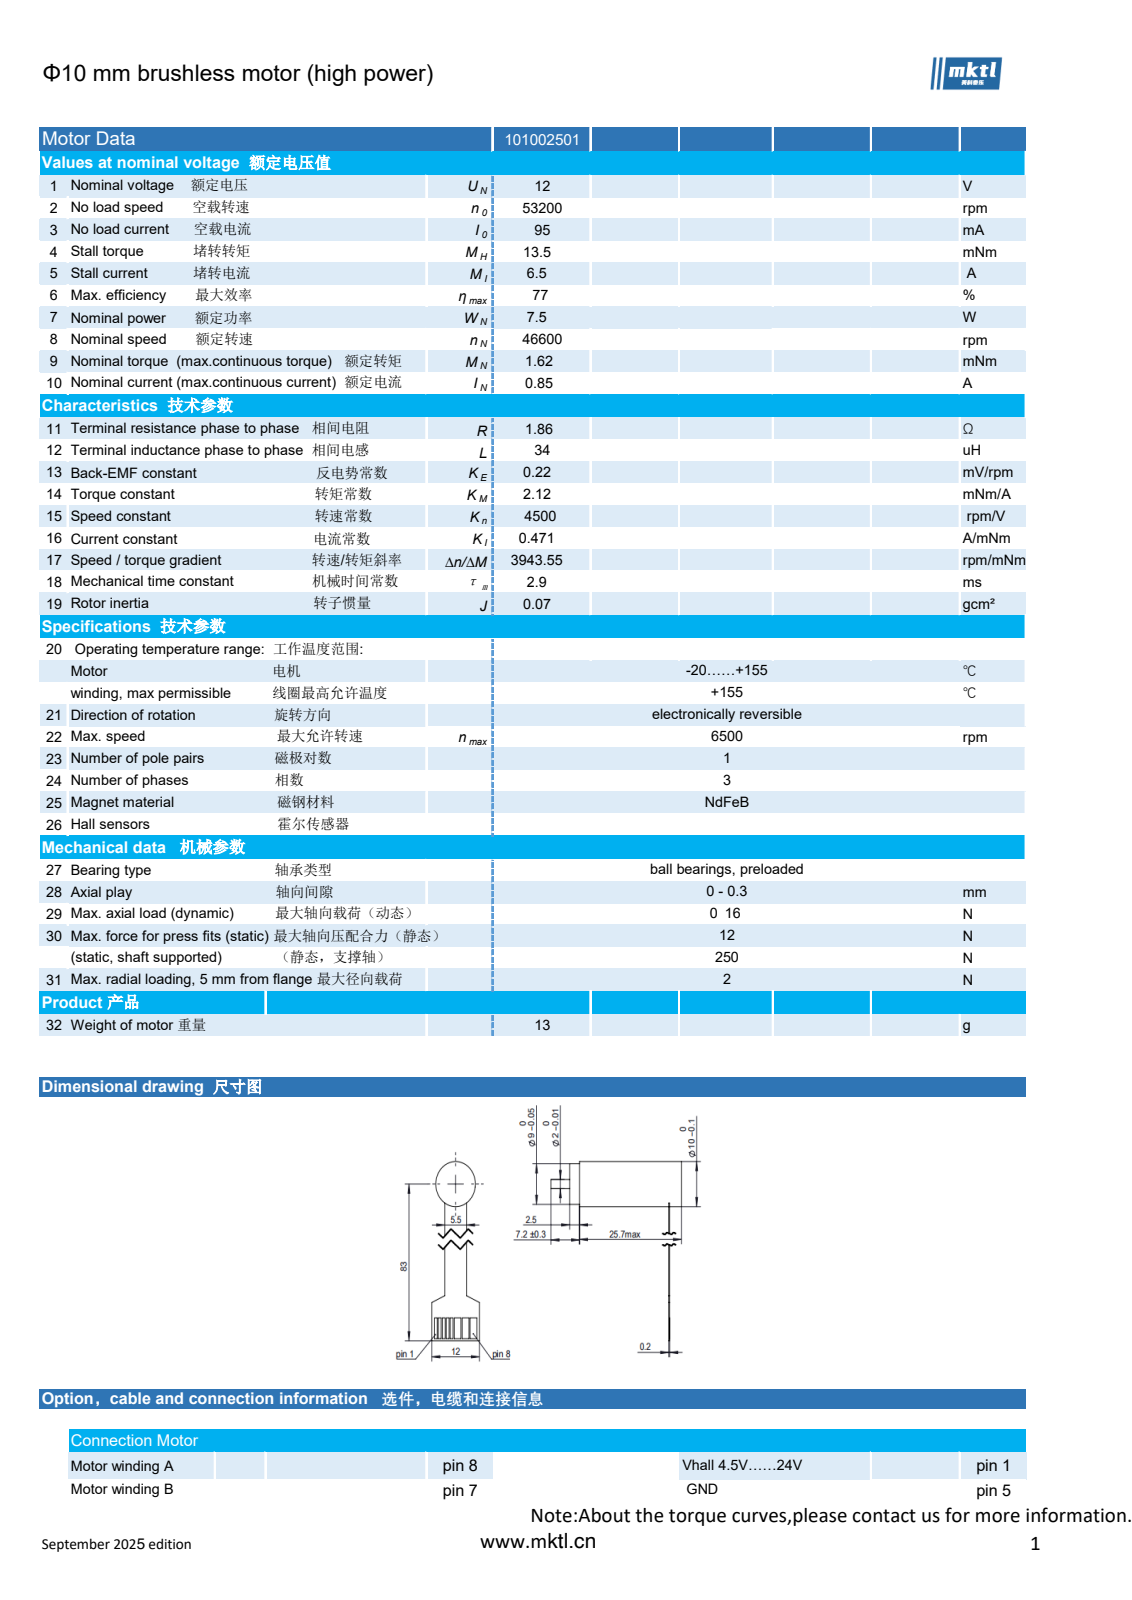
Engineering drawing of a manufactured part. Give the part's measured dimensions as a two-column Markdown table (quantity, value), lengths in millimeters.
| quantity | value |
| --- | --- |
| part name | 101002501 |
| STEP written by | SolidWorks 2018 (CONFIG_CONTROL_DESIGN) |
| units | millimeters |
| bodies | 1 solid, 59 faces (53 planar, 6 cylindrical, 0 other) |
| overall size | 88 × 32.3 × 12 |
| volume | 2 245 mm³ |
| surface area | 2 065 mm² |
| round bosses / shafts (diameter × count) | 10 × 1, 9 × 1, 2 × 1 |
| main face-to-face distances | 3, 3.2, 24.4, 24.6, 27.6, 24.65, 2.95, 2.5, 21.9, 22.1 |
